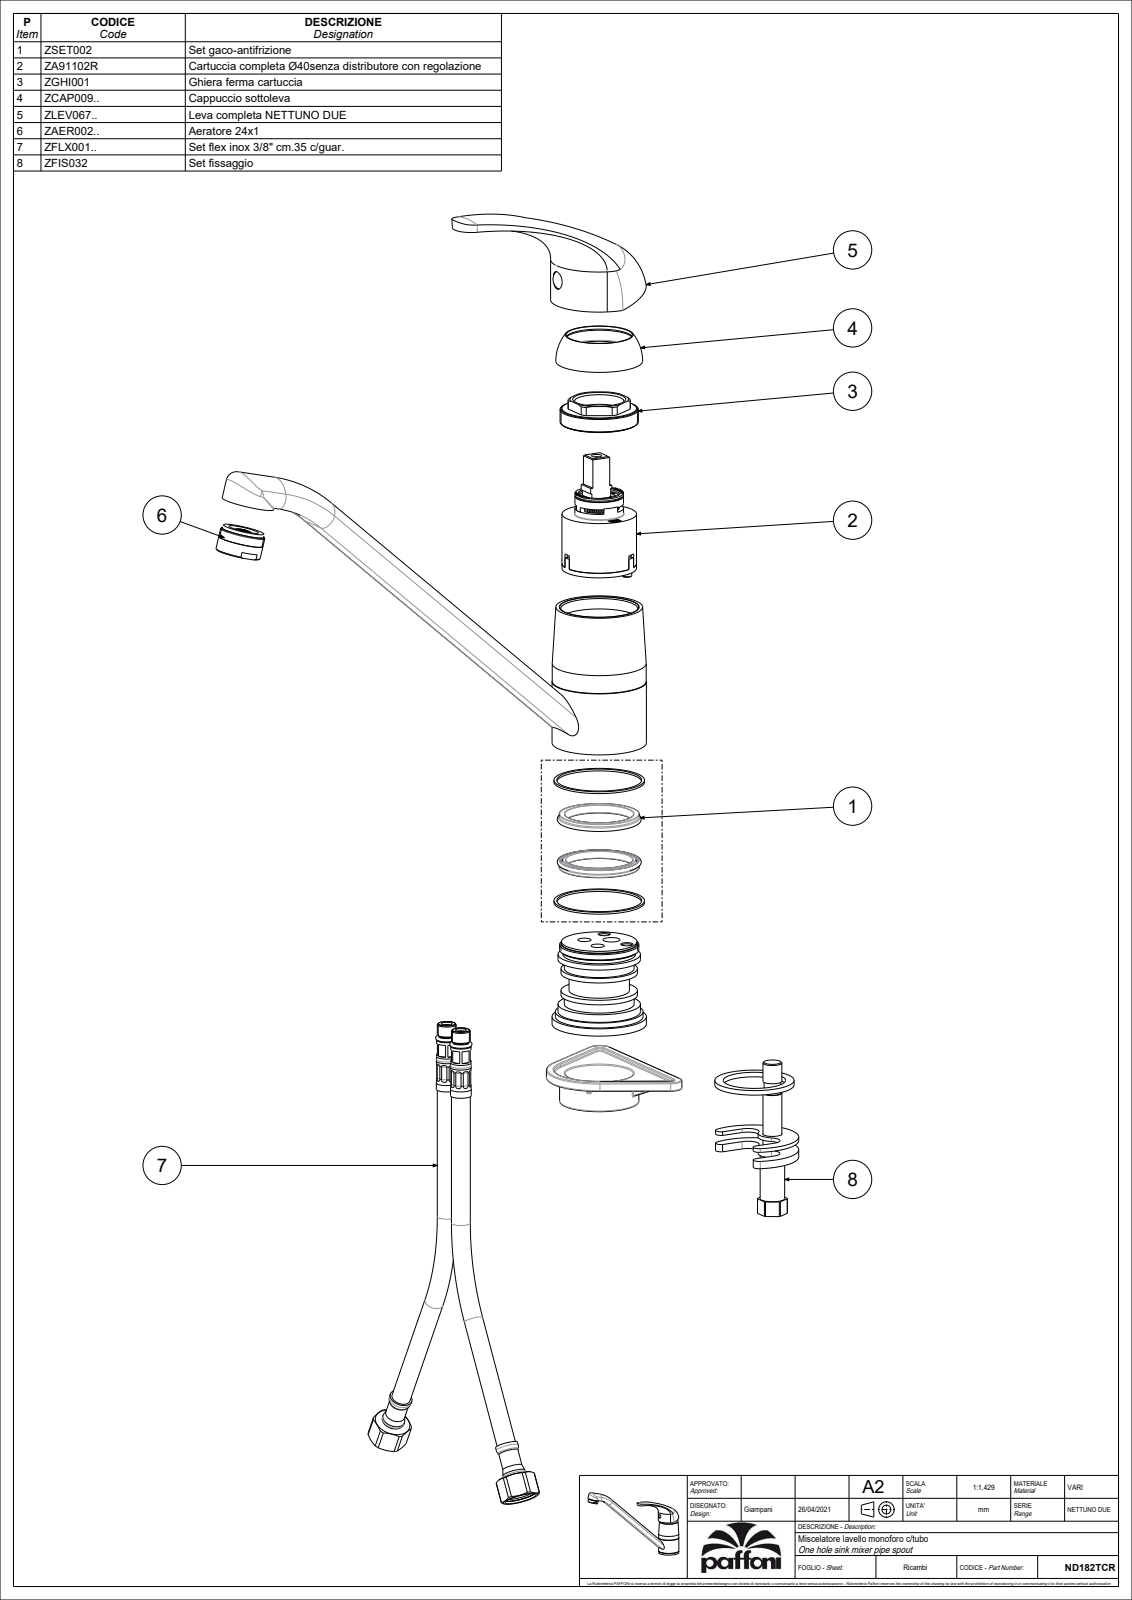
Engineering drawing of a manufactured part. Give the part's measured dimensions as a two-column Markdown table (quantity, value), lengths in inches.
| quantity | value |
| --- | --- |
| part name | ND182TCR |
| STEP written by | CREO PARAMETRIC BY PTC INC, 2020044 (CONFIG_CONTROL_DESIGN) |
| units | inches |
| bodies | 2 solids, 246 faces (74 planar, 91 cylindrical, 81 other) |
| overall size | 9.981 × 7.18 × 2.008 |
| volume | 13 in³ |
| surface area | 124.2 in² |
| round holes (diameter × count) | 0.354 × 5, 0.217 × 2, 0.276 × 2, 0.433 × 2, 0.236 × 1, 0.364 × 1, 1.378 × 1, 1.602 × 1, 1.61 × 1, 1.732 × 1, 1.748 × 1, 1.87 × 1 |
| round bosses / shafts (diameter × count) | 1.969 × 1, 1.961 × 1, 1.831 × 1, 1.764 × 1, 1.72 × 1, 1.594 × 1, 1.575 × 1, 1.457 × 1 |
| partial cylindrical surfaces (radius × count) | 0.217 × 4, 0.65 × 2, 0.154 × 1, 0.157 × 1, 0.981 × 1, 2.559 × 1 |
| main face-to-face distances | 3.676, 0.051, 0.05, 0.295, 1.78, 1.778, 1.728, 0.768, 0.098, 0.669 |
| hole center spacings | 0.044, 0.335, 0.339, 0.474, 0.483, 0.541, 0.564, 0.572 |
